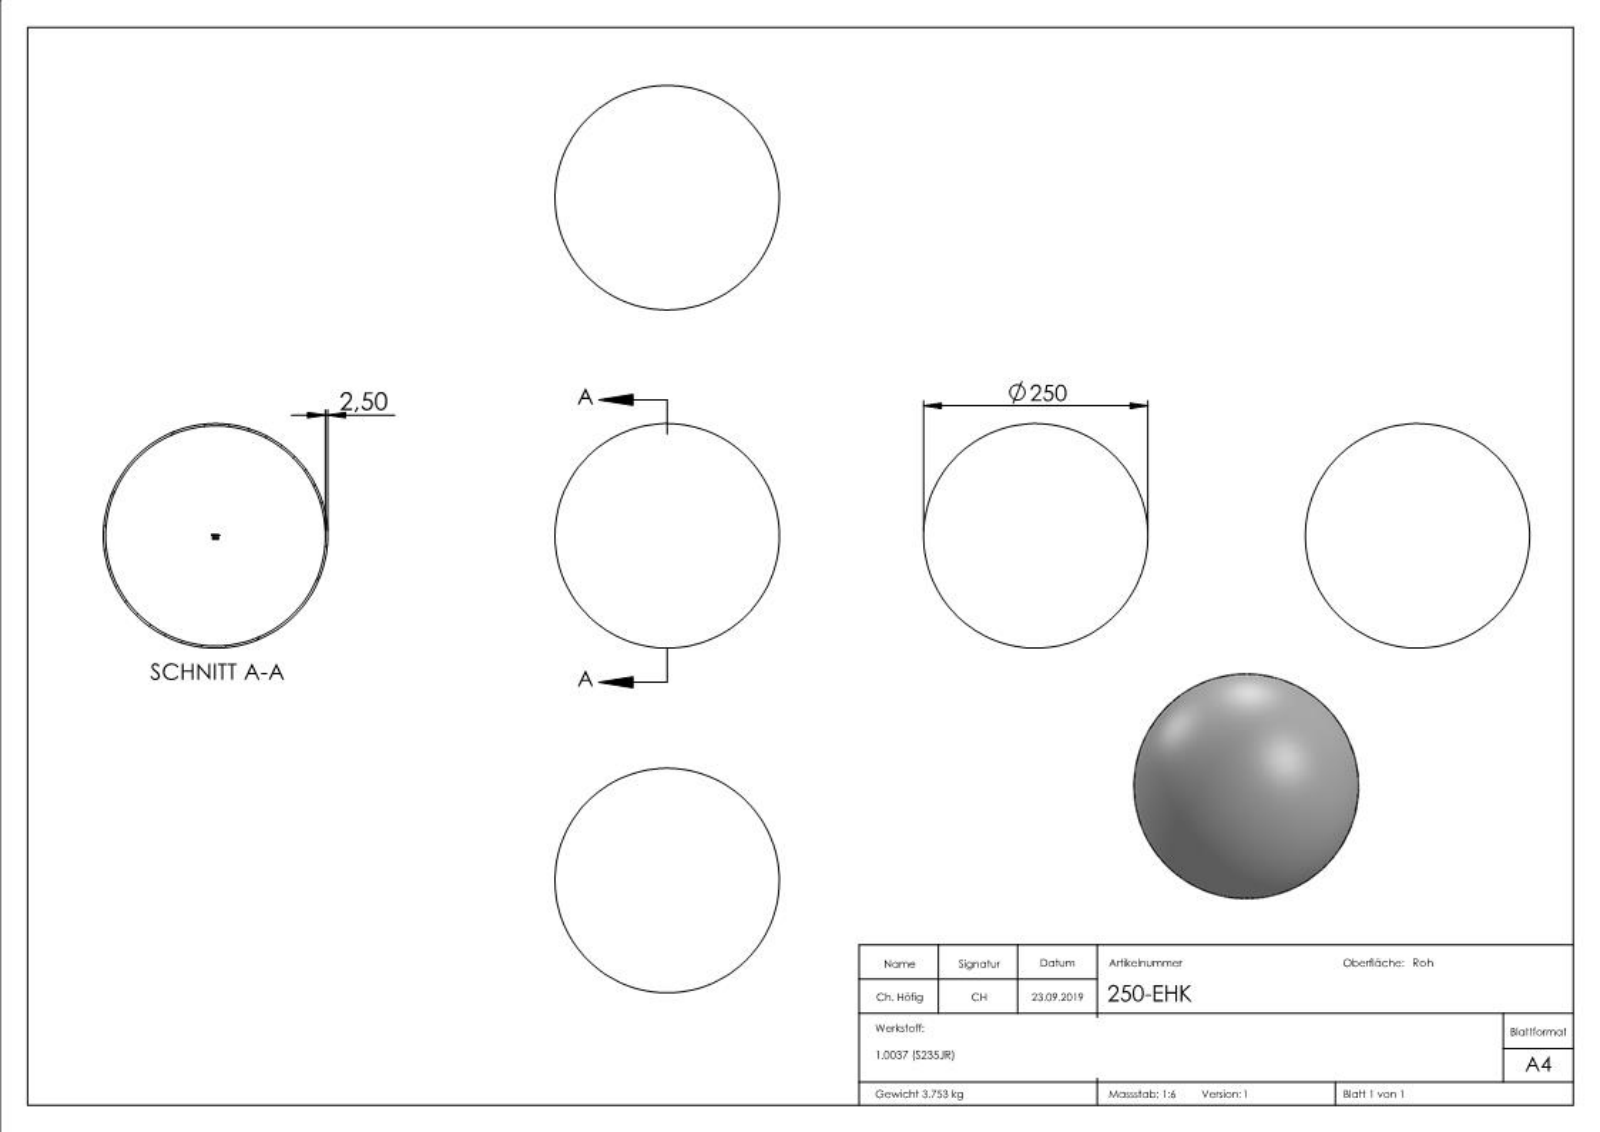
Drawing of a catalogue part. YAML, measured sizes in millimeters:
part_name: "250-EHK"
step_written_by: "SolidWorks 2015 (CONFIG_CONTROL_DESIGN)"
units: millimeters
bodies: {solids: 1, faces: 201, planar: 105, cylindrical: 0, other: 96}
overall_size: [250, 250, 250]
volume: 481121
surface_area: 384932
face_to_face_distances: [3.2, 1.26, 4.5, 0.46, 3.59, 3.13, 0.68, 1.32, 0.54, 0.64]
